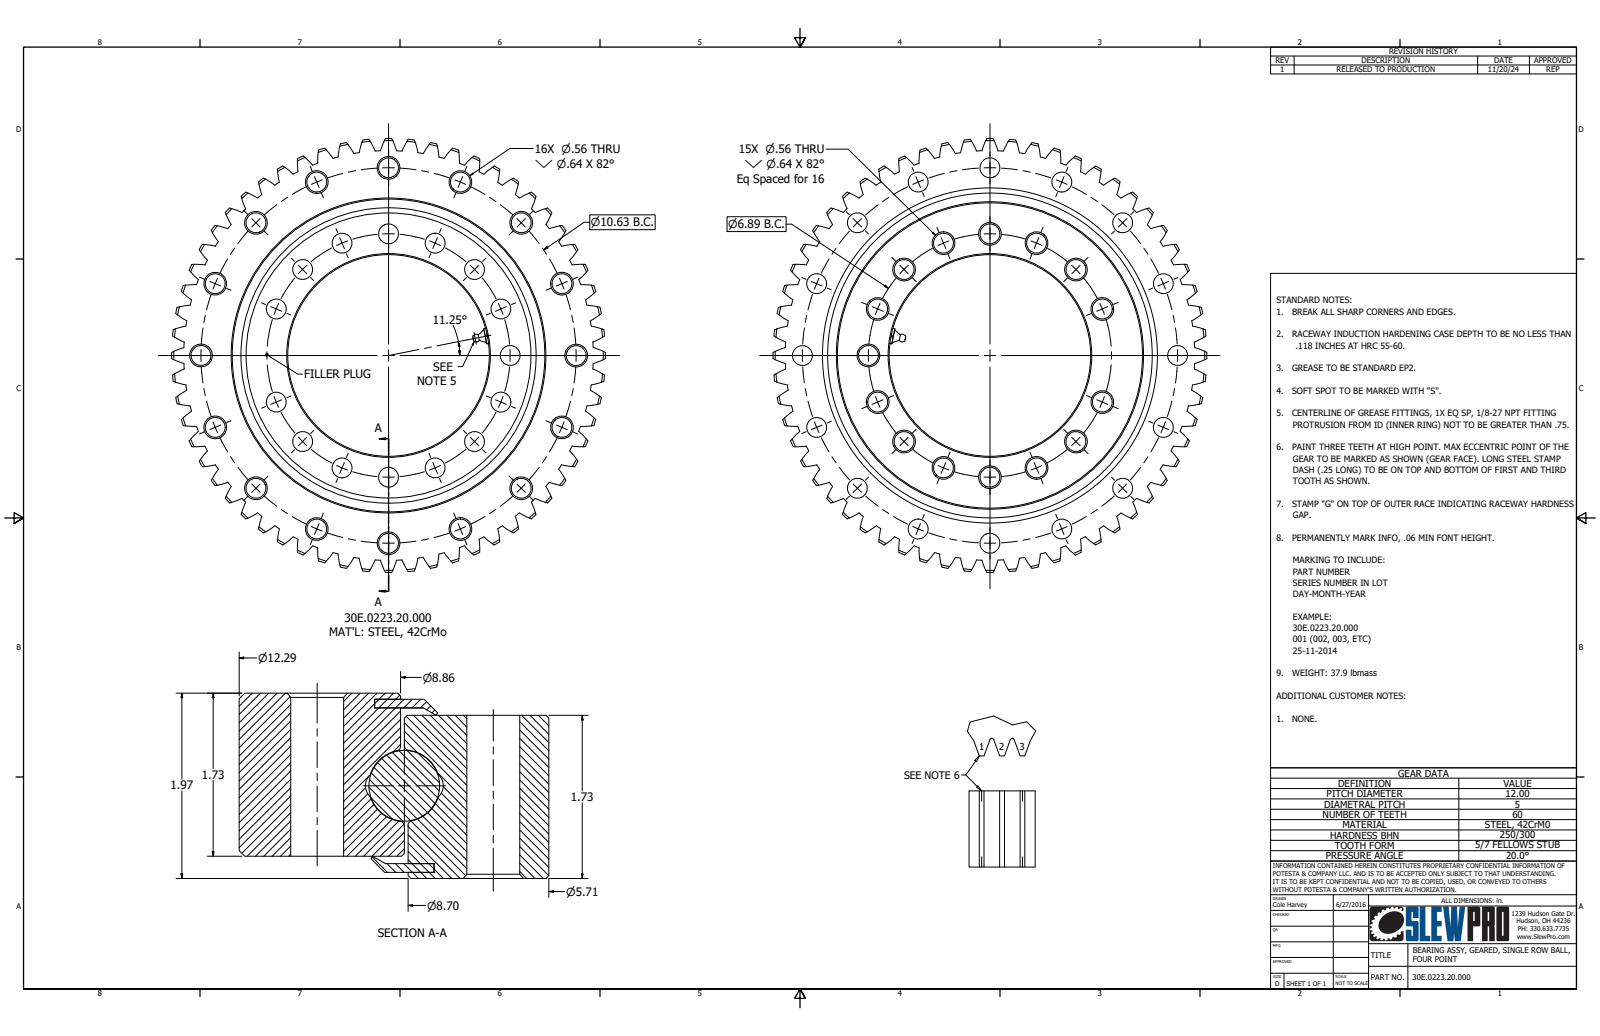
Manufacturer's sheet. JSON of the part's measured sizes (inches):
{"part_name": "30E.0223.20.000; Spur Gears1; 1_8 NPT Fitting", "step_written_by": "Autodesk Inventor 2024 (AUTOMOTIVE_DESIGN)", "units": "inches", "bodies": {"solids": 6, "faces": 587, "planar": 27, "cylindrical": 293, "other": 267}, "overall_size": [12.29, 12.29, 1.968], "volume_in3": 133.6, "surface_area_in2": 687.9, "round_holes": [[0.562, 31], [0.1, 1], [0.877, 1], [5.709, 1], [8.15, 1], [8.78, 1], [8.86, 1], [9.411, 1]], "round_bosses_or_shafts": [[9.41, 1], [8.78, 1], [8.7, 1], [8.149, 1], [0.875, 1]], "partial_cylinders_radius": [[1.852, 120], [4.64, 1], [5.8, 1], [6.145, 1]], "face_to_face_distances": [1.732, 0.236, 1.746, 0.093, 0.065, 1.903, 0.171, 1.667, 0.157, 1.811], "hole_center_spacings": [3.772, 8.6, 5.11, 3.445, 7.358, 1.344, 2.508, 4.872]}
